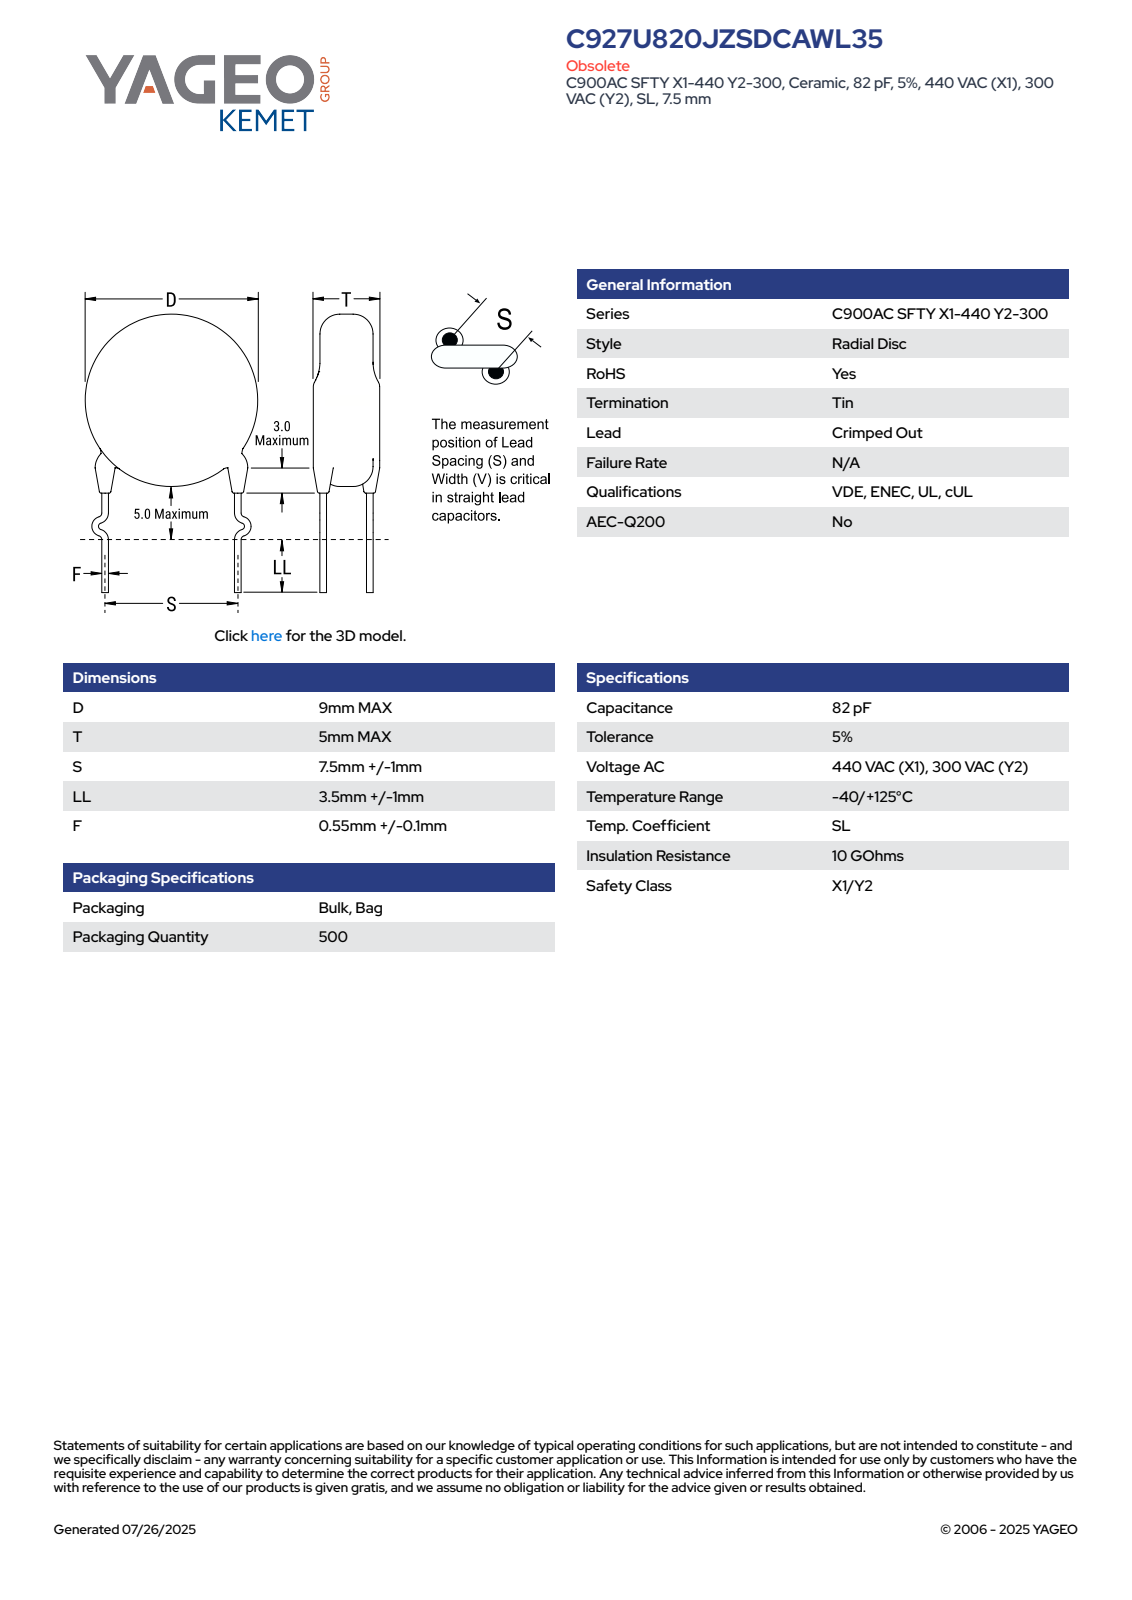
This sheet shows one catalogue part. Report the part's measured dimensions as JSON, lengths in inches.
{"part_name": "CCD_KCOC900_D9T5S7.5LL4.5F0.55", "step_written_by": "SolidWorks 2014 (AUTOMOTIVE_DESIGN)", "units": "inches", "bodies": {"solids": 4, "faces": 87, "planar": 63, "cylindrical": 6, "other": 18}, "overall_size": [0.728, 0.484, 0.197], "volume_in3": 0.019, "surface_area_in2": 0.481, "round_bosses_or_shafts": [[0.047, 2], [0.354, 1]], "face_to_face_distances": [0.197, 0.037, 0.196, 0.159, 0.03, 0.15, 0.023, 0.16, 0.109, 0.113]}
